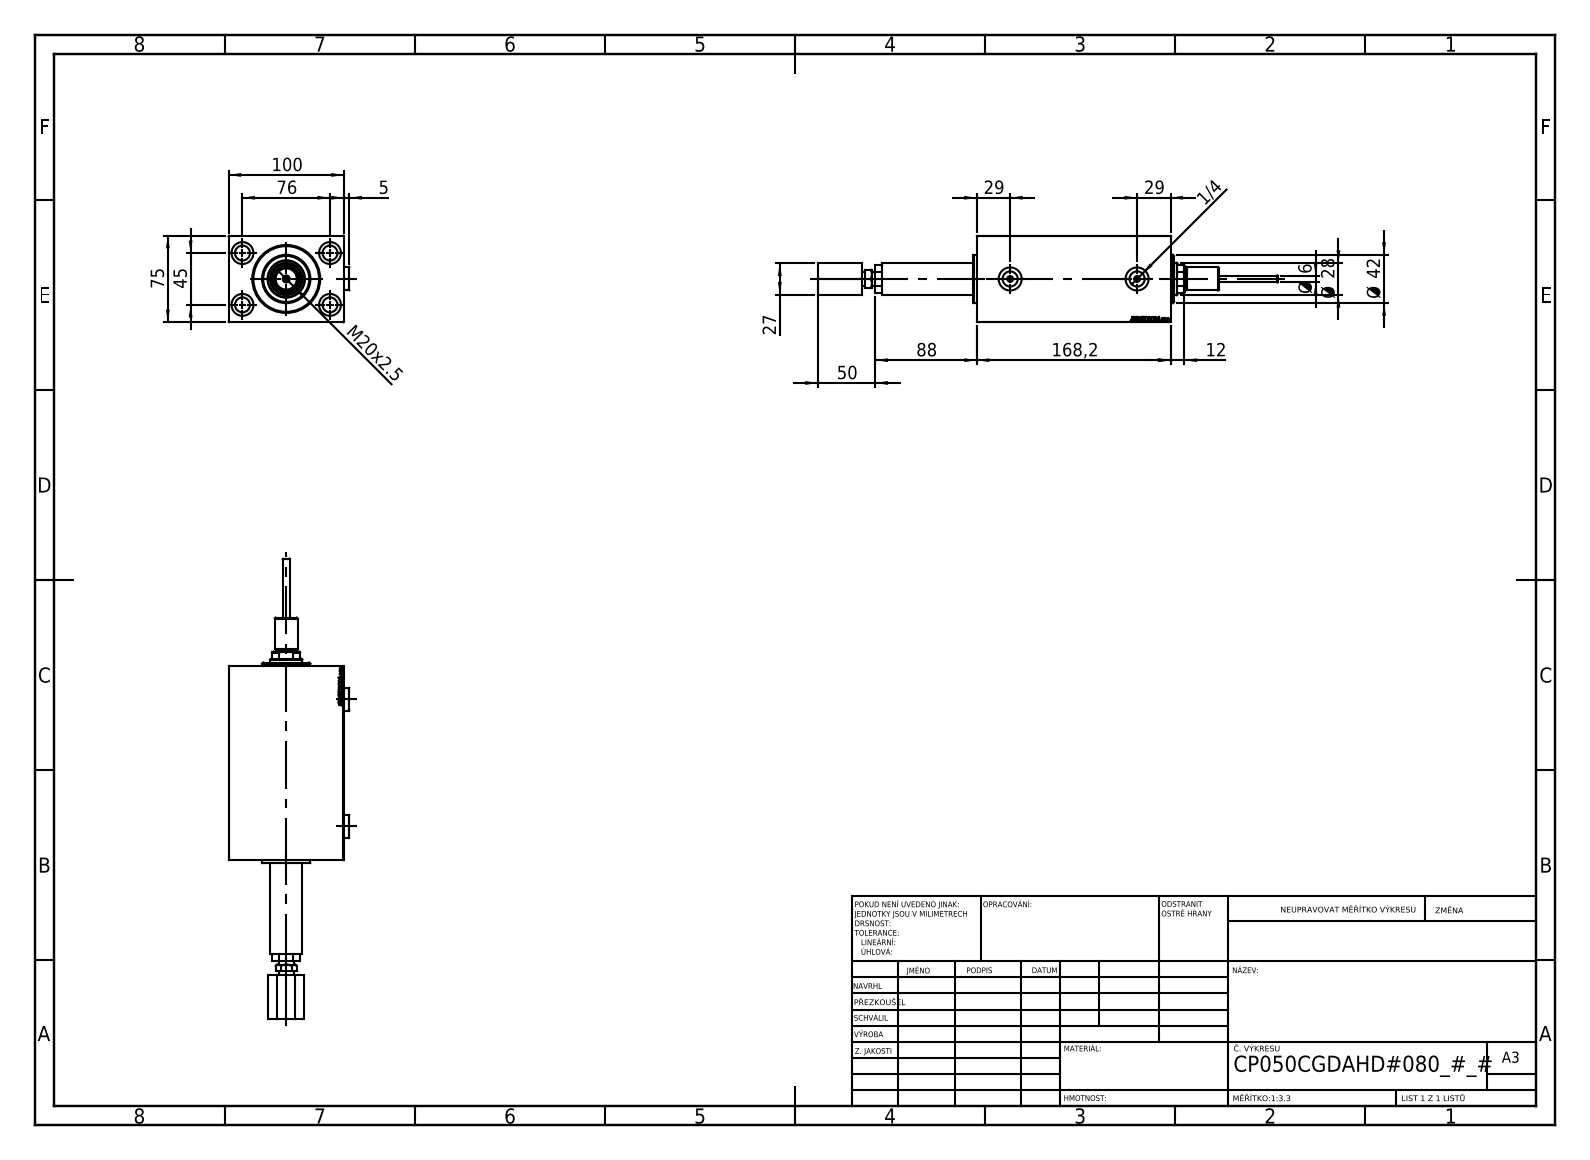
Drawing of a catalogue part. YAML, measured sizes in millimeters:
part_name: "V450DCP_C_Body; V450DCP_B_RodCooling_ACCESSORIES; V450DCP_VC_B; PLUG (+2 more)"
step_written_by: "SolidWorks 2019 (CONFIG_CONTROL_DESIGN)"
units: millimeters
bodies: {solids: 7, faces: 1024, planar: 480, cylindrical: 122, other: 422}
overall_size: [399.2, 104.9, 75]
volume: 1134000
surface_area: 198362
round_holes:
  - {diameter: 13, count: 4}
  - {diameter: 19, count: 4}
  - {diameter: 4, count: 2}
  - {diameter: 5, count: 2}
  - {diameter: 9.73, count: 2}
  - {diameter: 13.16, count: 2}
  - {diameter: 15, count: 2}
  - {diameter: 20, count: 2}
  - {diameter: 3, count: 1}
  - {diameter: 6, count: 1}
  - {diameter: 18.5, count: 1}
  - {diameter: 28, count: 1}
round_bosses_or_shafts:
  - {diameter: 42, count: 1}
  - {diameter: 20, count: 1}
  - {diameter: 18, count: 1}
  - {diameter: 12.78, count: 1}
partial_cylinders:
  - {radius: 13.5, count: 1}
face_to_face_distances: [75, 100, 154.2, 168.2, 14, 13, 1, 167.2, 27, 110]
hole_center_spacings: [44.16, 45, 76, 88.32, 42.55, 110.2]
